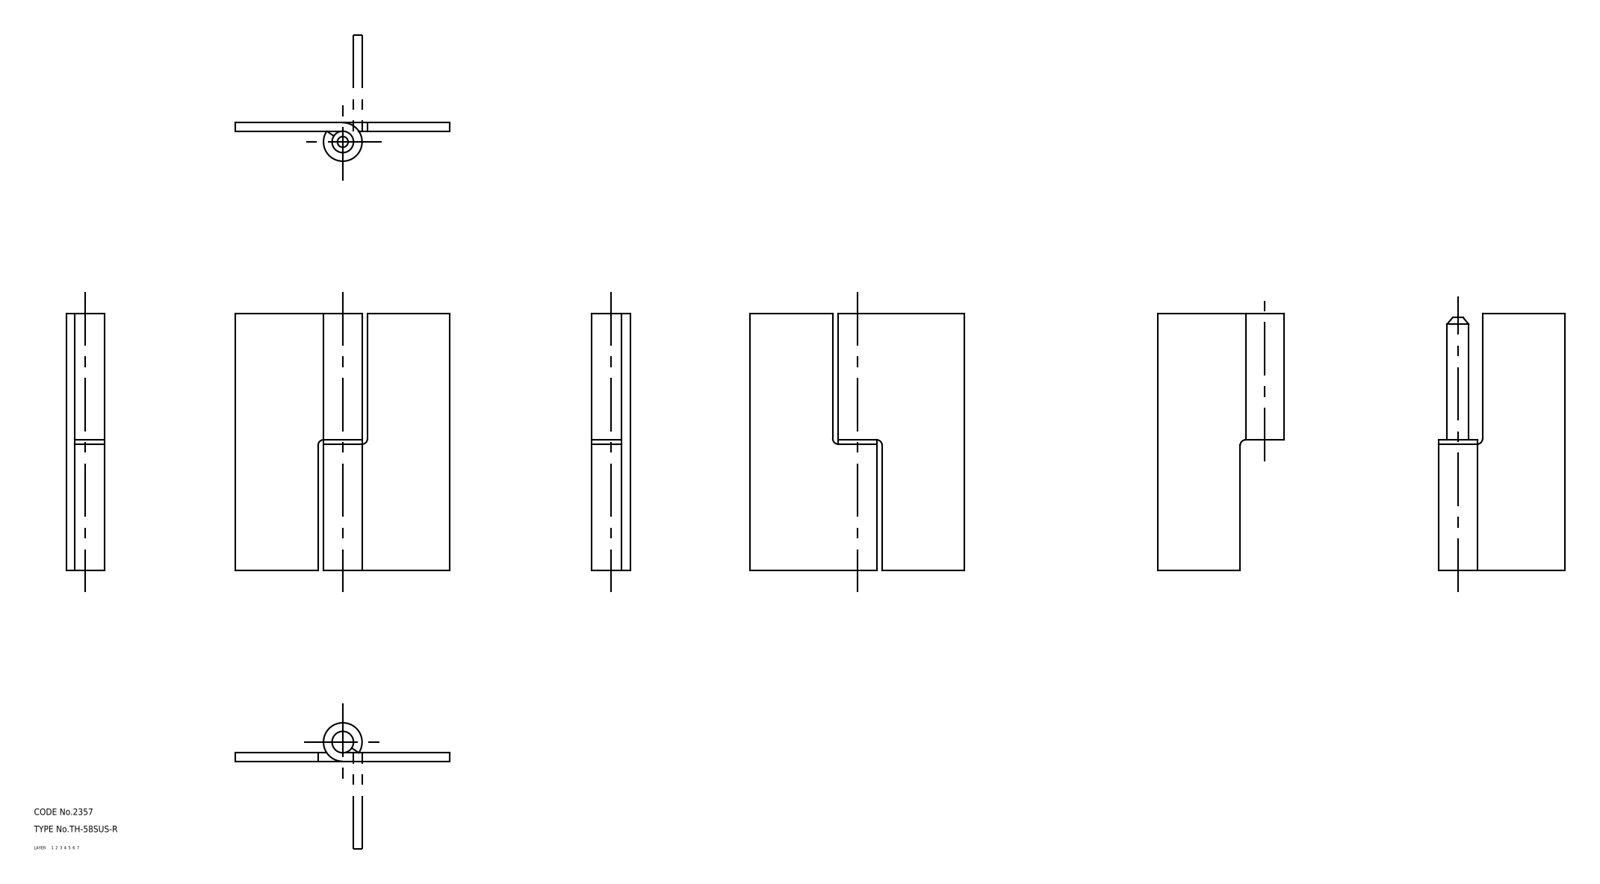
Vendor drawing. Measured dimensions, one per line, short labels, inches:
name: washer; shaft; hinge piece_B; hinge piece_A (+1 more)
written by: CADfix (AUTOMOTIVE_DESIGN)
unit: in
bodies: 4 solids, 34 faces (0 planar, 0 cylindrical, 34 other)
size: 4.724 × 3.937 × 0.709
volume: 4.237 in³; area: 58.24 in²
